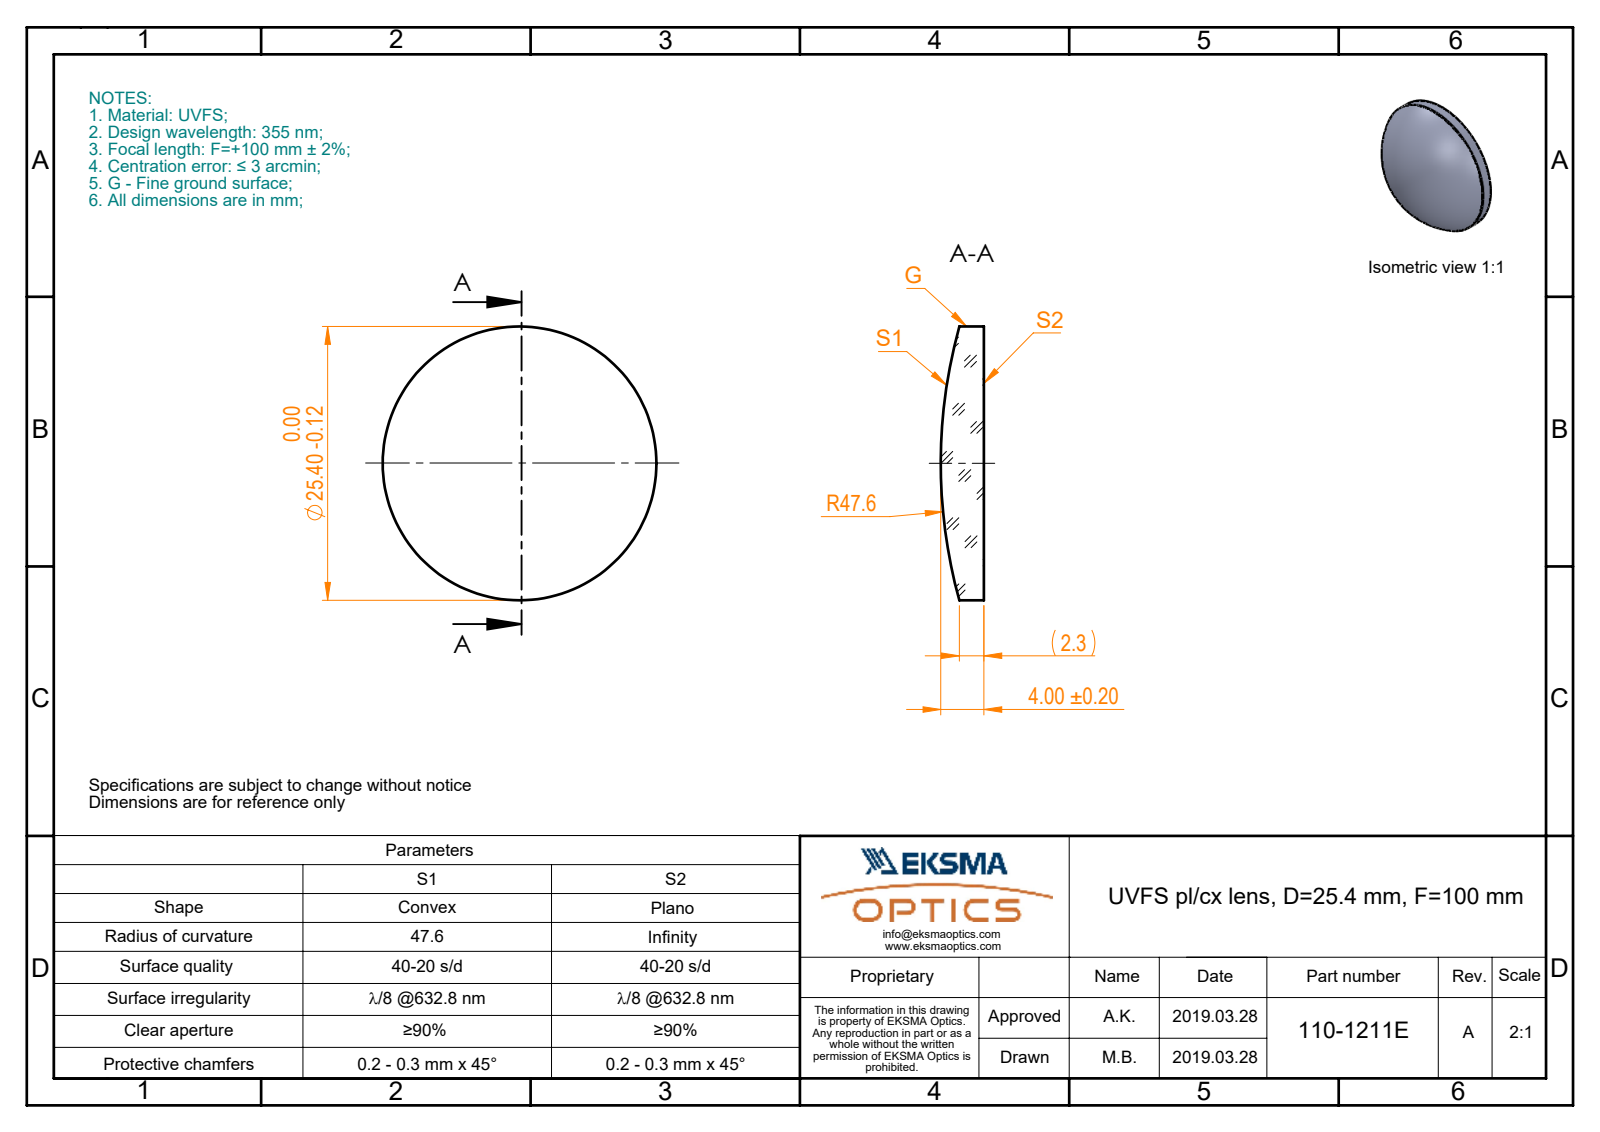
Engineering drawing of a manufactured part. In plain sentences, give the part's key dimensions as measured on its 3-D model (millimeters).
The part is named "110-1211E UVFS pl-cx 25.4 F100". Its 3-D file was written by "SolidWorks 2017 (CONFIG_CONTROL_DESIGN)". It is 1 solid with 5 faces: 1 planar, 2 cylindrical and 2 other. Overall it measures 25.4 by 25.4 by 4 millimeters. Its volume is 1 592 cubic millimeters and its surface area 1 204 square millimeters. Round bosses or shafts: 1 of diameter 25.4.
